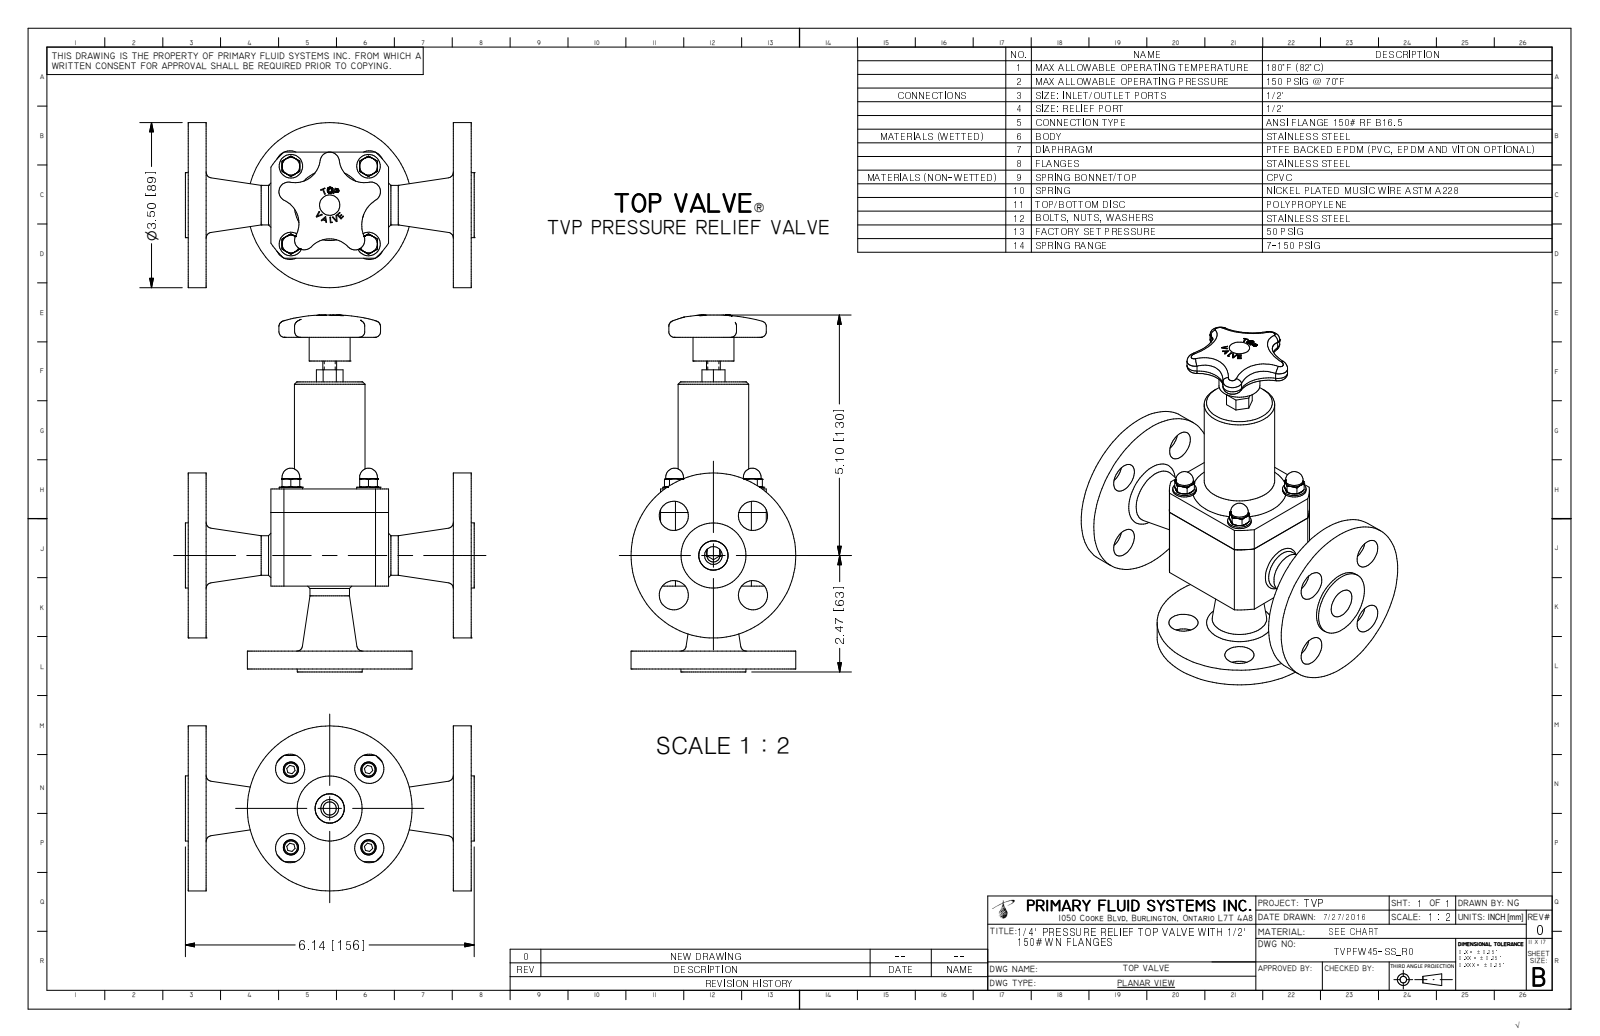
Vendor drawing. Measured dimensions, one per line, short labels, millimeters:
name: TVPFW45-SS_R0
written by: Autodesk Inventor 2009 (AUTOMOTIVE_DESIGN)
unit: mm
bodies: 1 solid, 392 faces (156 planar, 69 cylindrical, 167 other)
size: 192.3 × 156 × 88.9
volume: 461 000 mm³; area: 93 480 mm²
holes: 8× ⌀15.7, 4× ⌀3.7, 2× ⌀15.8, 1× ⌀38.7
bosses: 4× ⌀12.7, 4× ⌀9.5, 4× ⌀7.9, 2× ⌀88.9, 2× ⌀35.1, 2× ⌀21.3, 1× ⌀38.1, 1× ⌀22.1
rounds: 5× R2.2, 5× R5.2, 4× R13.6, 4× R16.7, 1× R15.9, 1× R18.9, 1× R37.8
face distances: 9.7, 143.1, 152.8, 133.5, 44.6, 108.1, 35, 98.5, 44.6, 35
hole spacings: 30.2, 42.7, 42.3, 59.9, 60.5, 0.6, 0.6, 29.6
